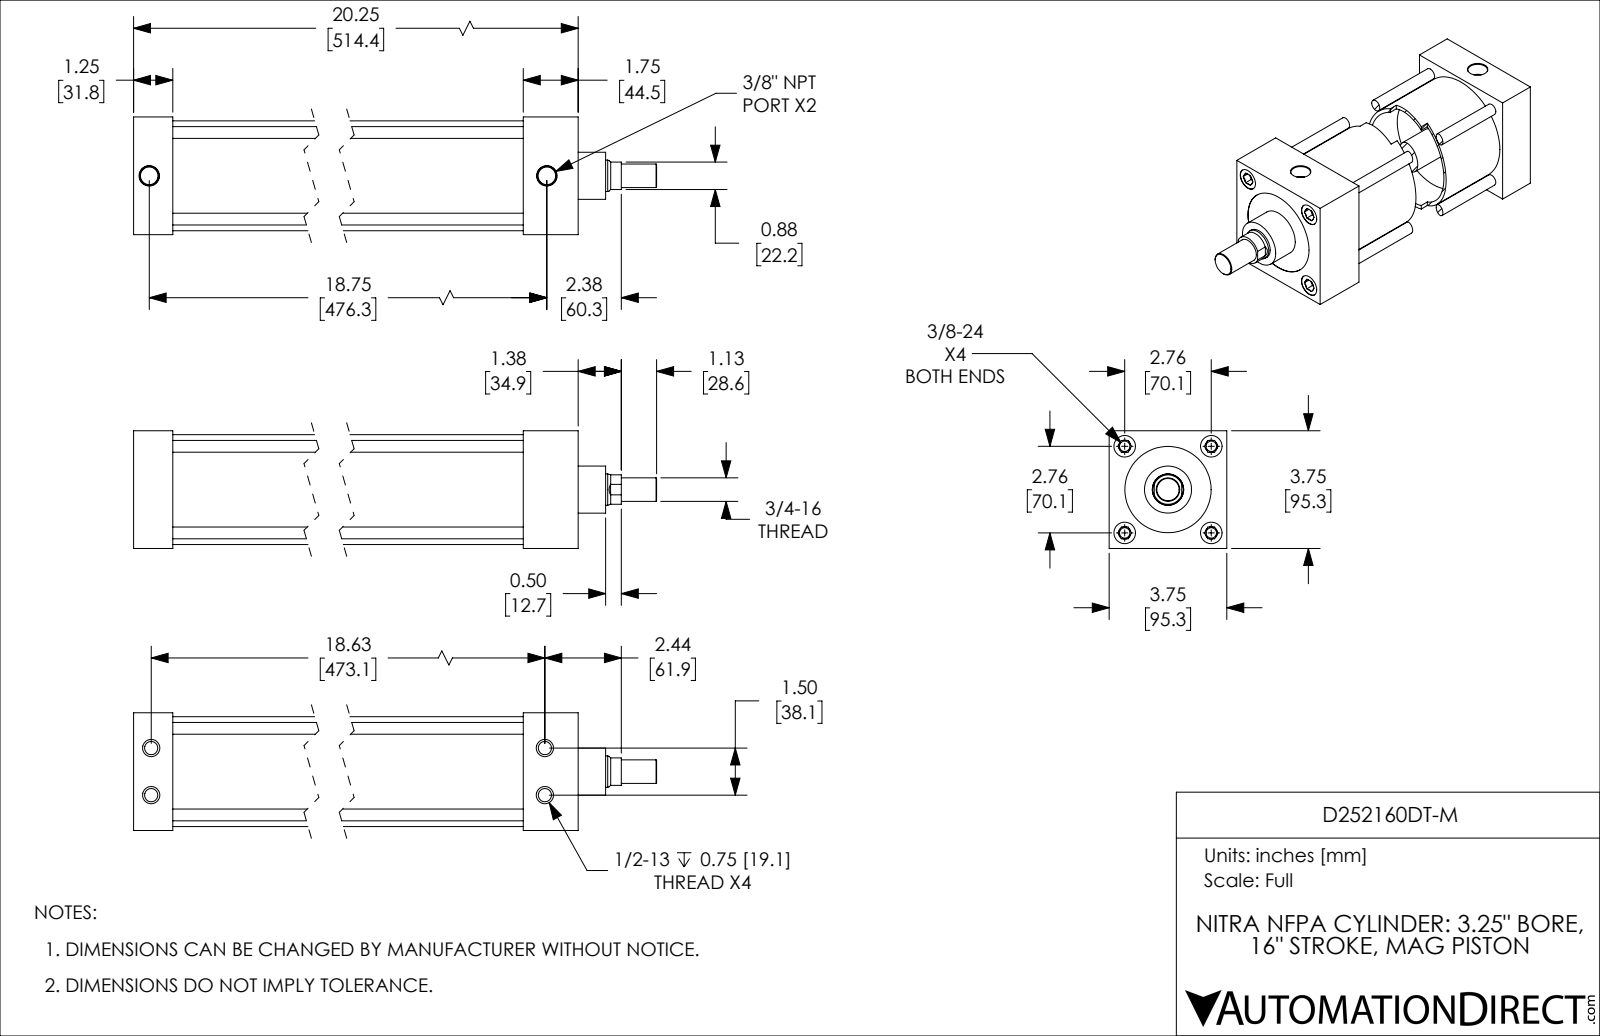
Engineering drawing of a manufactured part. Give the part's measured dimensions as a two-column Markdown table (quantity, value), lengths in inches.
| quantity | value |
| --- | --- |
| part name | D252160DT-M_PISTON_KK1; D252160DT-M; D252160DT-M_BODY |
| STEP written by | SolidWorks 2019 (CONFIG_CONTROL_DESIGN) |
| units | inches |
| bodies | 2 solids, 198 faces (58 planar, 62 cylindrical, 78 other) |
| overall size | 22.75 × 3.75 × 3.75 |
| volume | 95.76 in³ |
| surface area | 666.4 in² |
| round holes (diameter × count) | 0.332 × 4, 0.422 × 4, 0.687 × 4, 0.562 × 2, 1 × 1, 2.75 × 1, 3.251 × 1 |
| round bosses / shafts (diameter × count) | 0.375 × 4, 3.501 × 1, 3.249 × 1, 1.5 × 1, 0.999 × 1, 0.75 × 1 |
| partial cylindrical surfaces (radius × count) | 0.469 × 1 |
| main face-to-face distances | 1.25, 3.75, 18.5, 17.25, 2.5, 16, 20.25, 19, 17.75, 1.75 |
| hole center spacings | 0.753, 1.952, 2.76, 18.702, 1.5, 3.903, 18.625, 18.685 |
